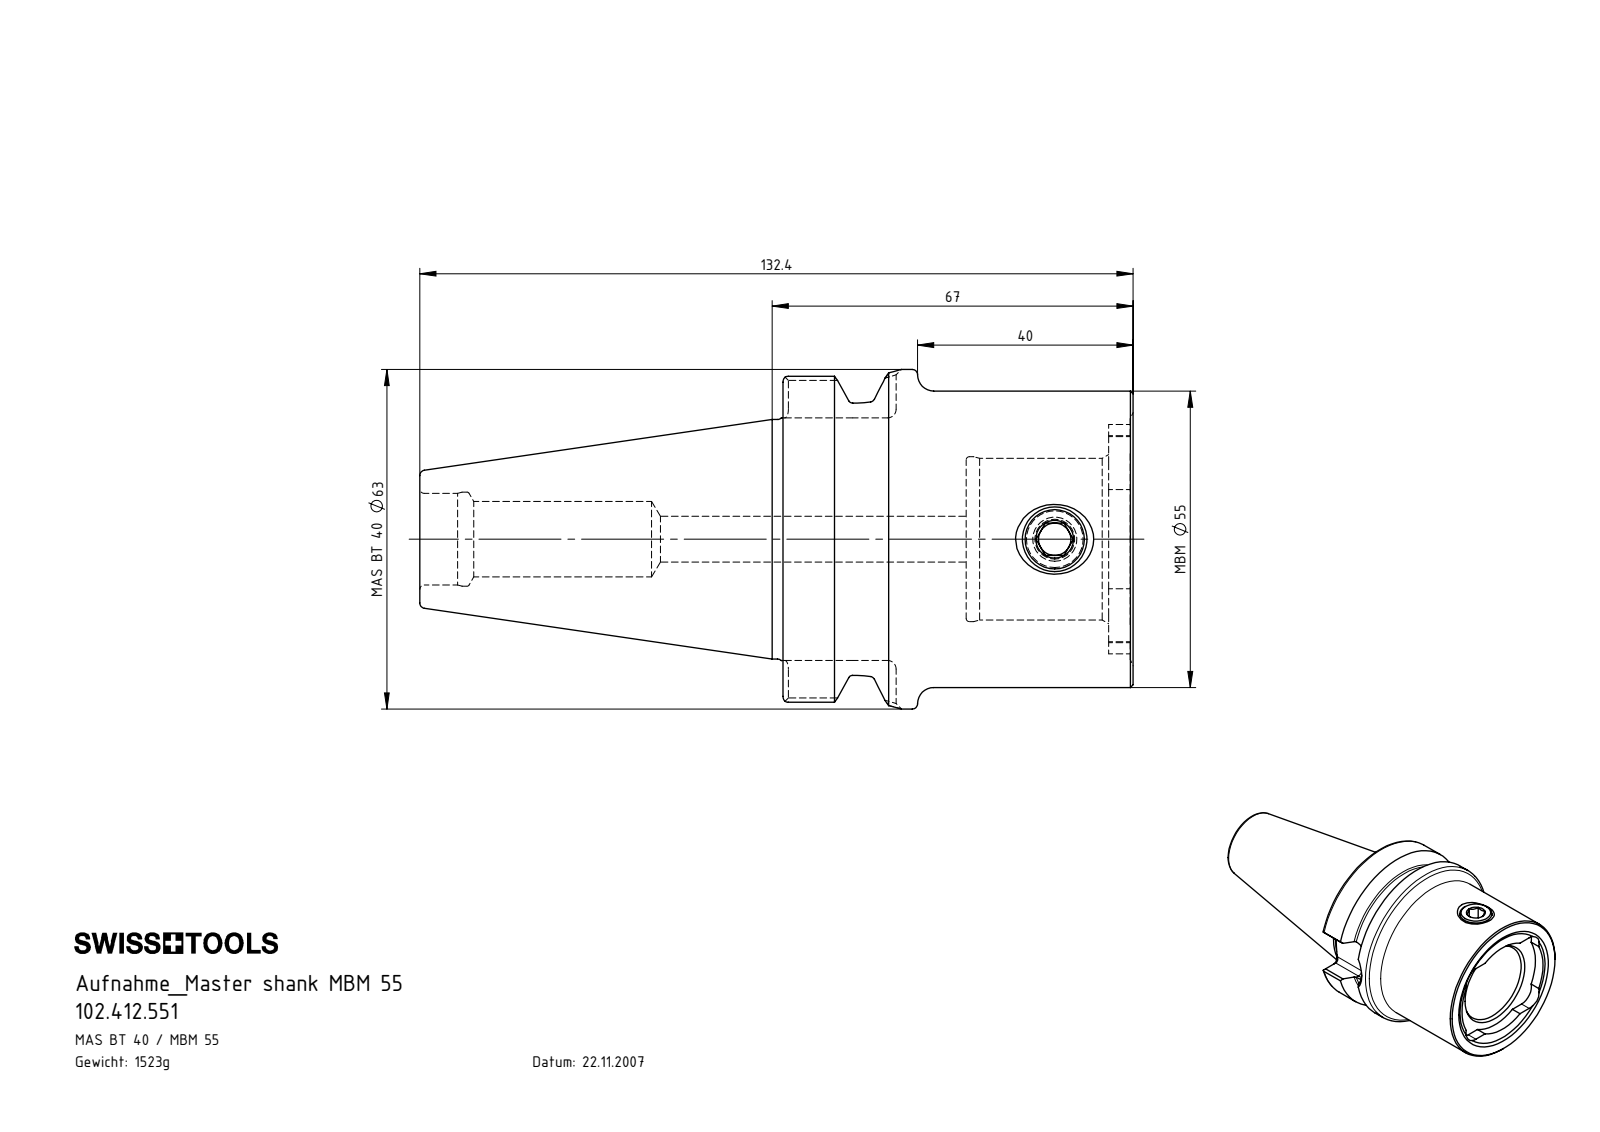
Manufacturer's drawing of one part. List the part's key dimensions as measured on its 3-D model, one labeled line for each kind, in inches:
Part name (STEP PRODUCT): ISO 4026 - M5 x 5_PreviewCfg; MB5-ER1.001.017_A; 102.412.551; BB4-MB5.K01.067_B (+1 more)
STEP written by: SolidWorks 2017 (CONFIG_CONTROL_DESIGN)
Units: inches
Bodies: 5 solids, 221 faces (69 planar, 71 cylindrical, 81 other)
Overall size (bounding box): 5.213 × 2.48 × 2.48
Volume: 11.82 in³ · Surface area: 51.73 in²
Round holes (diameter × count): ⌀0.165 ×3, ⌀0.13 ×2, ⌀0.236 ×1, ⌀0.335 ×1, ⌀0.433 ×1, ⌀0.551 ×1, ⌀0.669 ×1, ⌀0.687 ×1, ⌀1.181 ×1, ⌀1.205 ×1
Round bosses / shafts (diameter × count): ⌀0.157 ×2, ⌀2.48 ×1, ⌀2.165 ×1, ⌀2.087 ×1, ⌀1.75 ×1, ⌀0.472 ×1, ⌀0.197 ×1
Partial cylindrical surfaces — rounded edges, fillets, slot ends (radius × count): R0.063 ×8, R0.205 ×4, R0.317 ×1, R0.474 ×1, R0.728 ×1, R0.837 ×1
Main face-to-face distances: 1.339, 2.559, 1.22, 2.38, 1.041, 0.179, 0.157, 2.537, 1.199, 0.022
